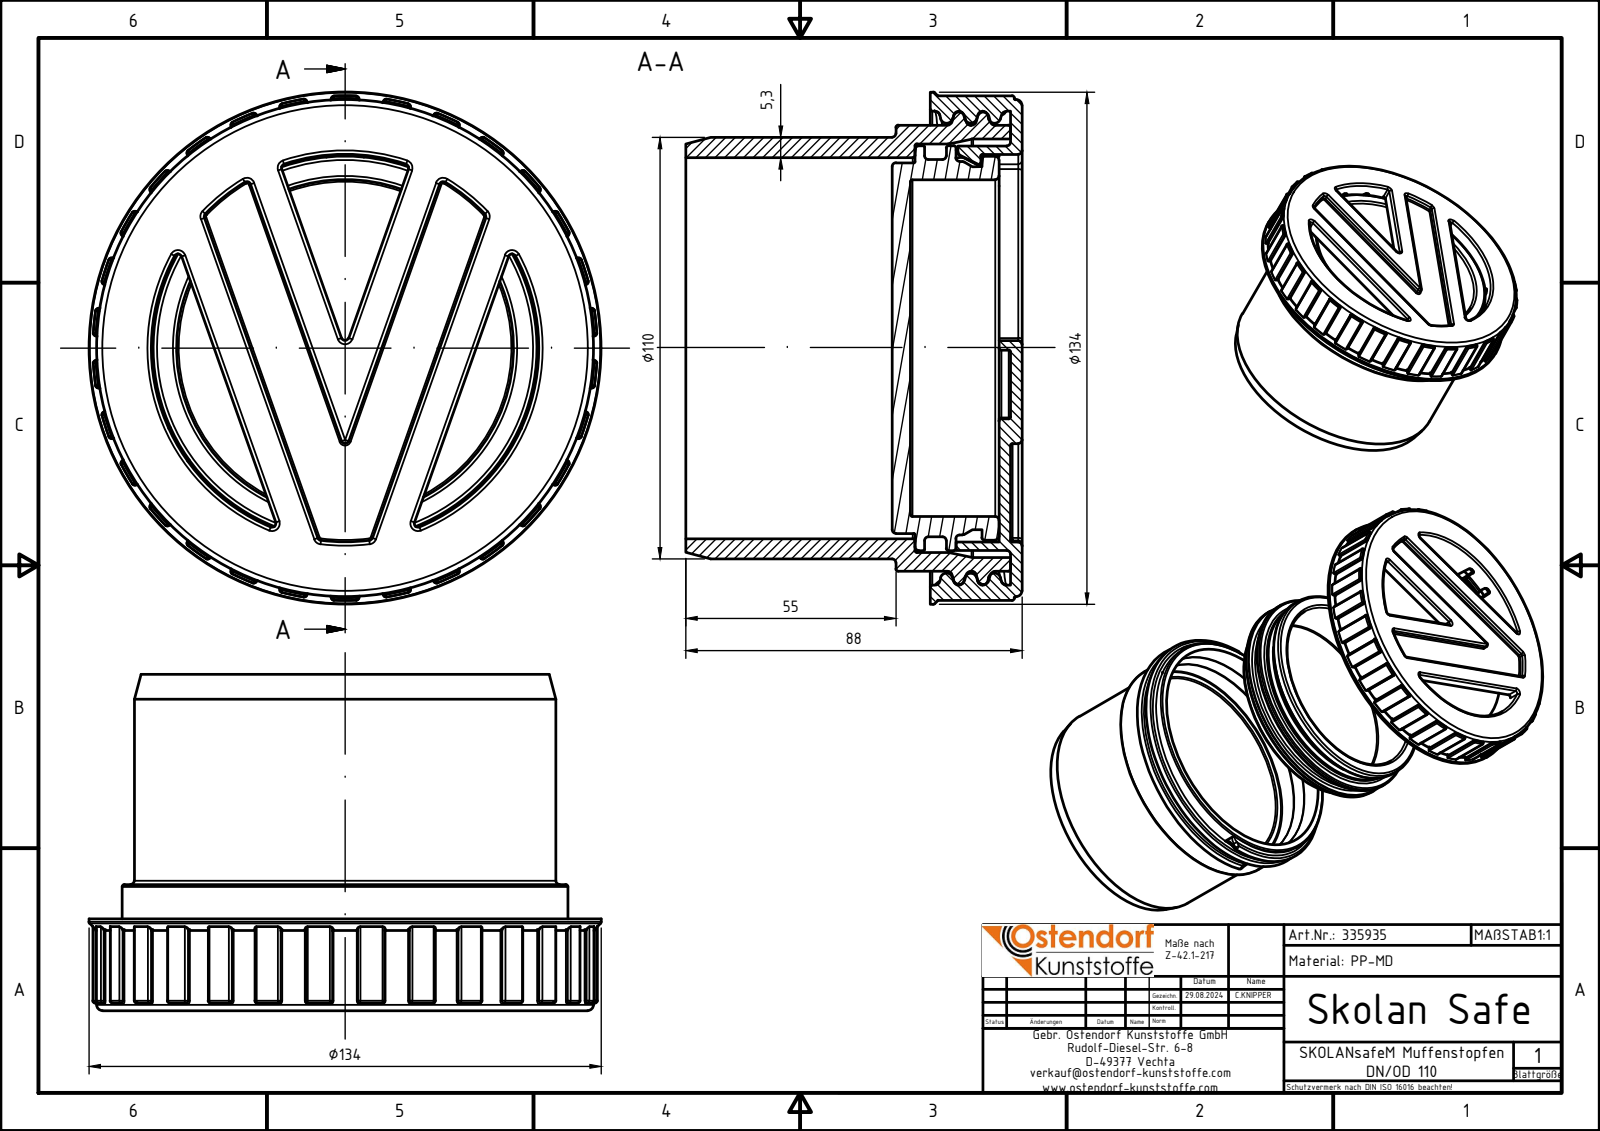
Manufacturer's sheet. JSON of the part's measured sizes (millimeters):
{"part_name": "335935z; 335935 Skolanreiniger; 335935 SkolanStrömungseinsatz; 335600_2 Deckel für Reiniger DN_OD 110", "step_written_by": "Autodesk Inventor 2024 (AUTOMOTIVE_DESIGN)", "units": "millimeters", "bodies": {"solids": 3, "faces": 958, "planar": 161, "cylindrical": 303, "other": 494}, "overall_size": [134, 134, 88], "volume_mm3": 314239, "surface_area_mm2": 156162, "round_holes": [[88.1, 1], [99.7, 1], [101.4, 1], [106.9, 1], [109.5, 1], [124, 1]], "round_bosses_or_shafts": [[134, 1], [130, 1], [116.65, 1], [110.3, 1], [105.9, 1], [105.8, 1], [100.4, 1], [98.7, 1]], "partial_cylinders_radius": [[0.6, 124], [0.3, 60], [1, 28], [0.5, 13], [0.4, 6], [1.2, 6], [2, 6], [3.5, 1]], "face_to_face_distances": [3, 31, 6, 28, 34, 4.8, 26.2, 29.2, 23.2, 2.5]}
